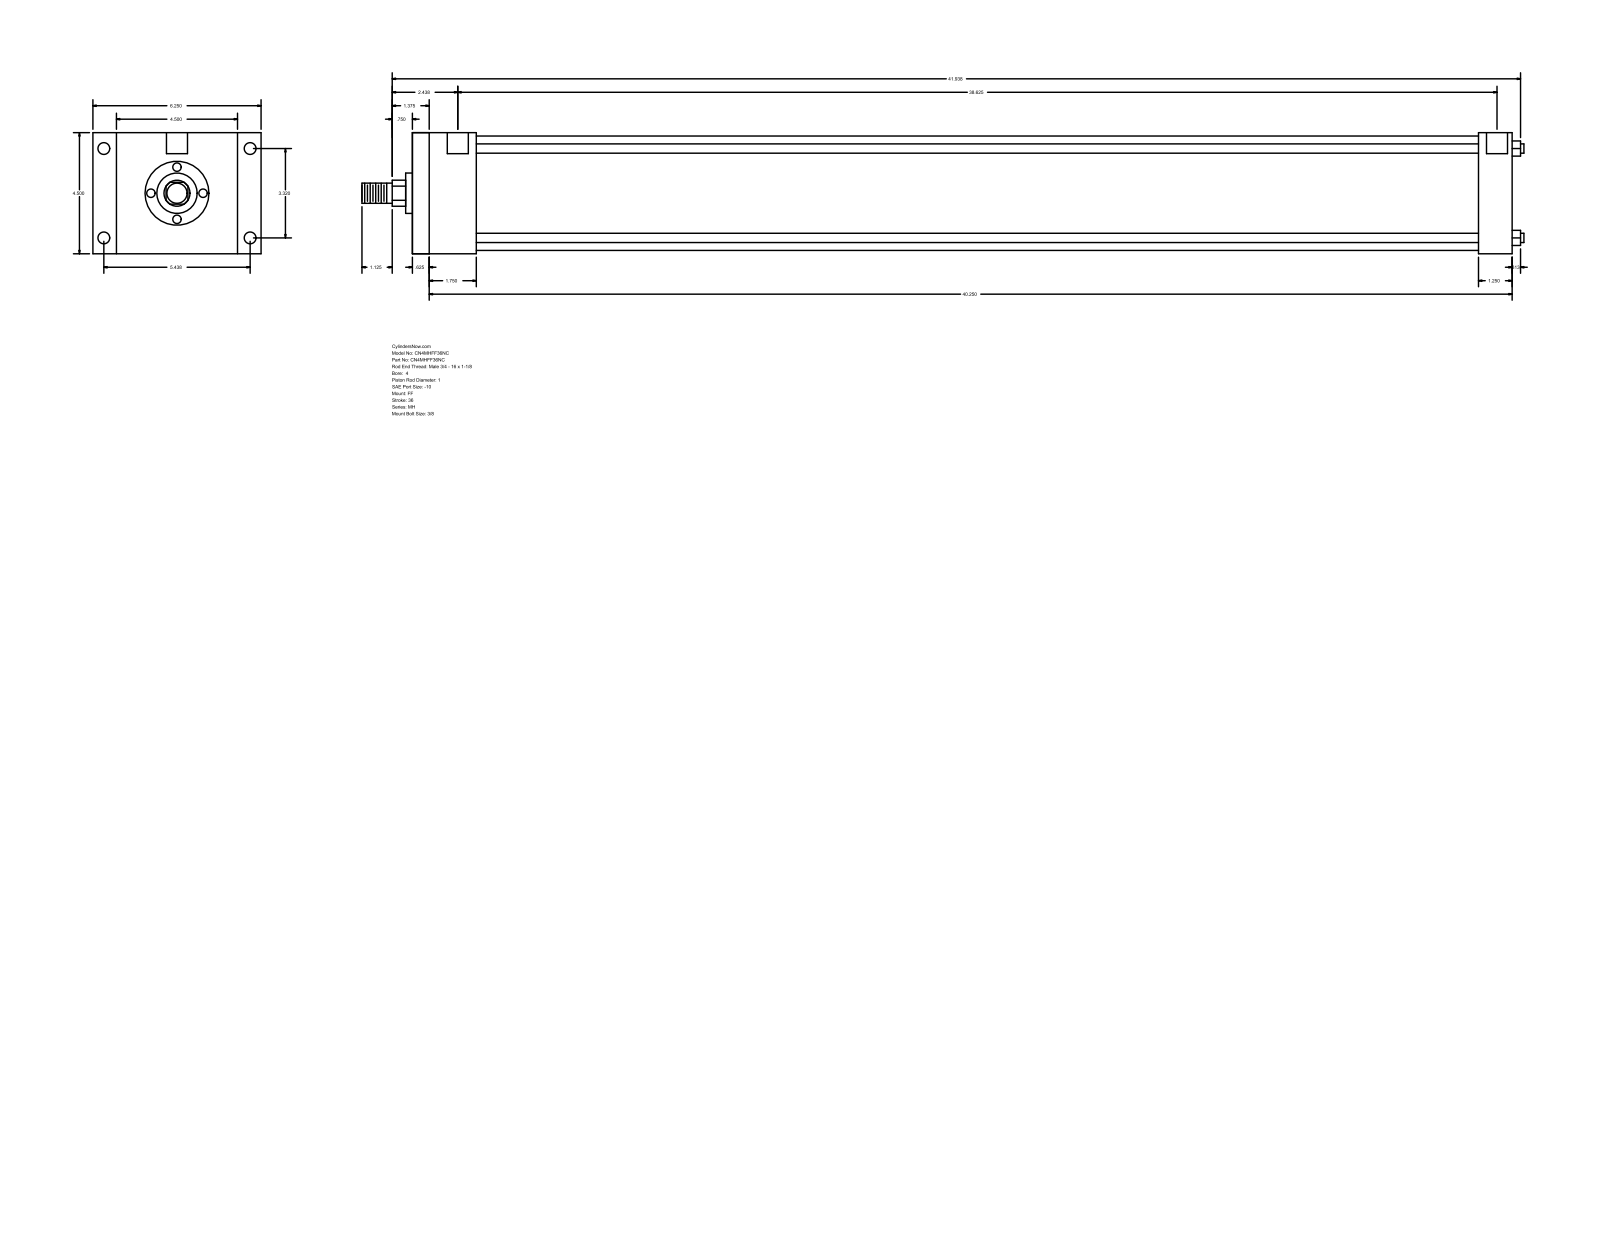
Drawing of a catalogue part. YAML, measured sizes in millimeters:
part_name: "MH_FF__0400_1"
step_written_by: "GSSL Pune (CONFIG_CONTROL_DESIGN)"
units: millimeters
bodies: {solids: 0, faces: 92, planar: 64, cylindrical: 28, other: 0}
overall_size: [1096.96, 158.75, 114.3]
round_holes:
  - {diameter: 8.73, count: 4}
  - {diameter: 11.13, count: 4}
  - {diameter: 19.84, count: 2}
round_bosses_or_shafts:
  - {diameter: 8.76, count: 4}
  - {diameter: 107.95, count: 1}
  - {diameter: 38.1, count: 1}
  - {diameter: 25.4, count: 1}
  - {diameter: 19.05, count: 1}
partial_cylinders:
  - {radius: 12.29, count: 1}
face_to_face_distances: [114.3, 1038.23, 15.87, 1022.36, 60.33, 44.46, 977.9, 1006.48, 990.61, 946.15]
hole_center_spacings: [84.32, 138.12, 161.82, 984.25, 1.58, 1.59, 981.08, 982.66]
